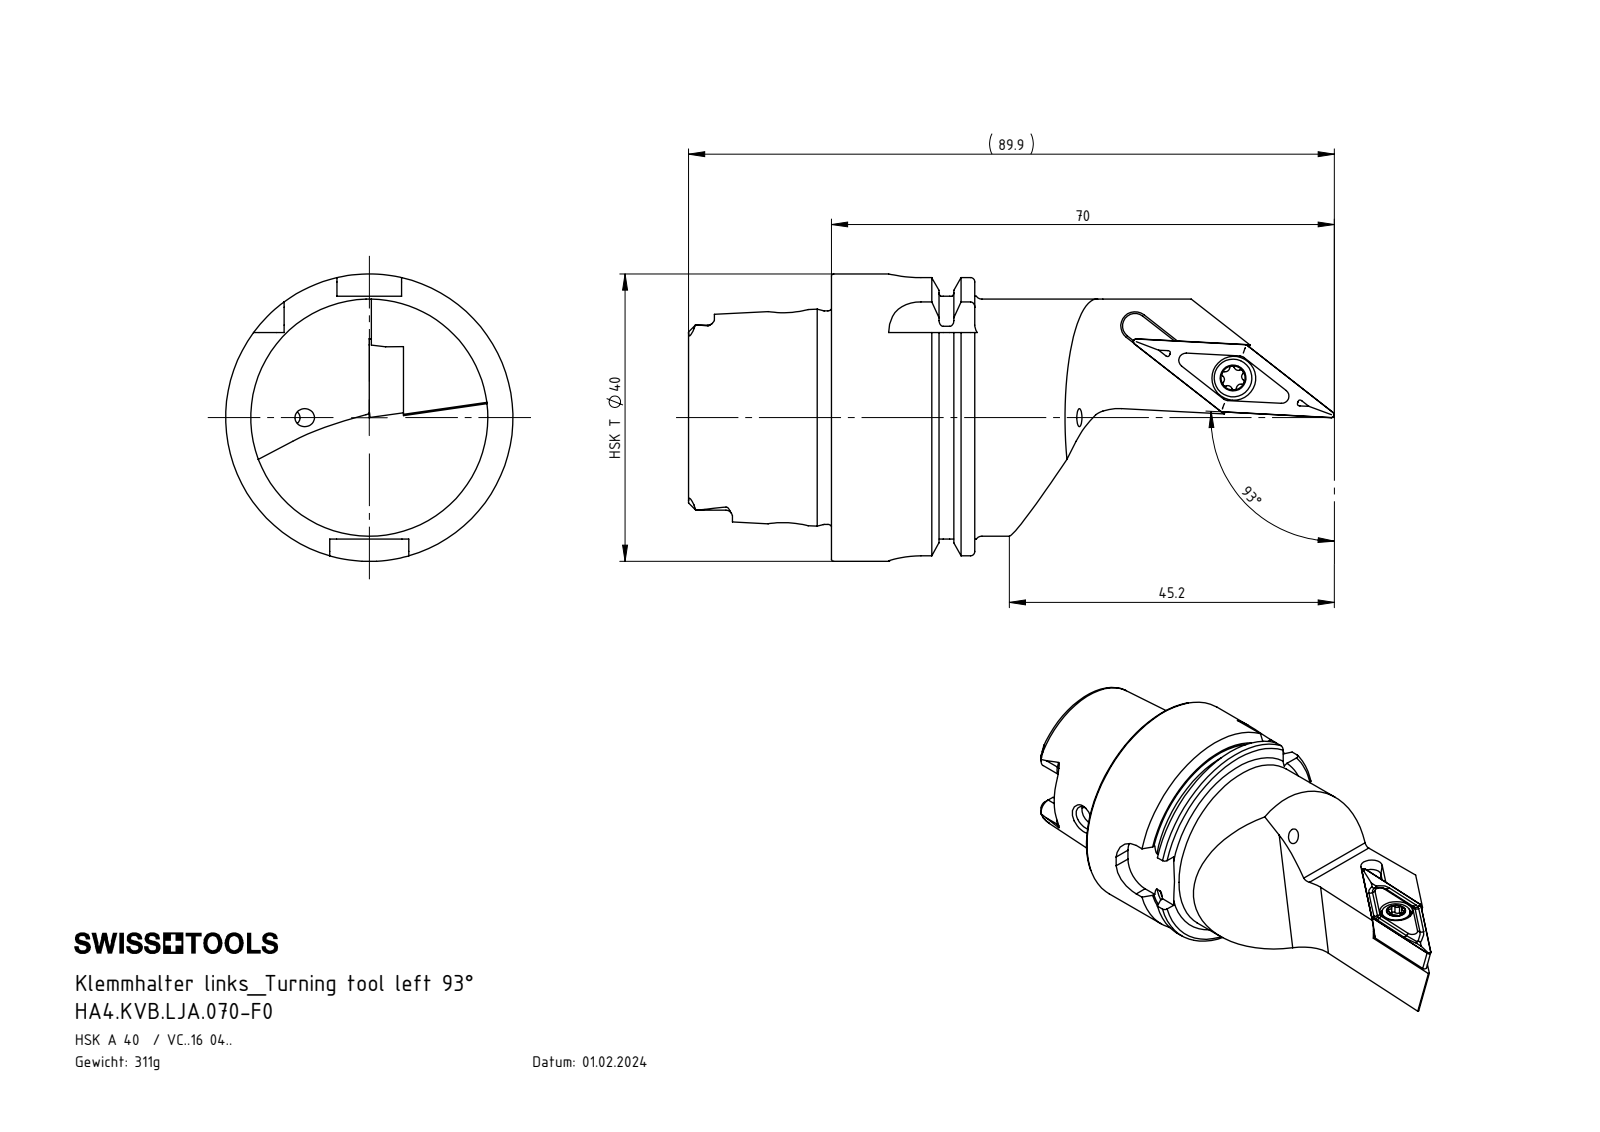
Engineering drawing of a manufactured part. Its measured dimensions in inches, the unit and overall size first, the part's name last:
Units: inches
Overall size (bounding box): 3.539 × 1.575 × 1.575
Round holes (diameter × count): ⌀0.13 ×2, ⌀0.098 ×1, ⌀0.165 ×1, ⌀0.173 ×1, ⌀0.181 ×1, ⌀0.197 ×1, ⌀0.24 ×1, ⌀0.394 ×1, ⌀0.433 ×1, ⌀0.492 ×1, ⌀0.827 ×1, ⌀1.004 ×1
Round bosses / shafts (diameter × count): ⌀0.157 ×2, ⌀1.575 ×1, ⌀1.368 ×1, ⌀1.299 ×1, ⌀1.17 ×1, ⌀0.207 ×1
Partial cylindrical surfaces — rounded edges, fillets, slot ends (radius × count): R0.013 ×6, R0.023 ×6, R0.035 ×6, R0.074 ×4, R0.177 ×4, R0.039 ×1, R0.069 ×1, R0.276 ×1
Main face-to-face distances: 0.313, 0.785, 0.472, 0.176, 1.096, 0.783, 1.569, 1.406, 0.622, 0.309
Hole centre spacings: 0.669, 1.274, 1.279, 1.937, 1.942
Volume: 2.358 in³ · Surface area: 21.02 in²
Bodies: 4 solids, 293 faces (88 planar, 84 cylindrical, 121 other)
Part name (STEP PRODUCT): HA4-KVB.LJA.070-F0_A; WCB-ER2.001.009_A; VCMT160404; ISO 4026 - M4 x 5 (+1 more)
STEP written by: SolidWorks 2022 (AUTOMOTIVE_DESIGN)
